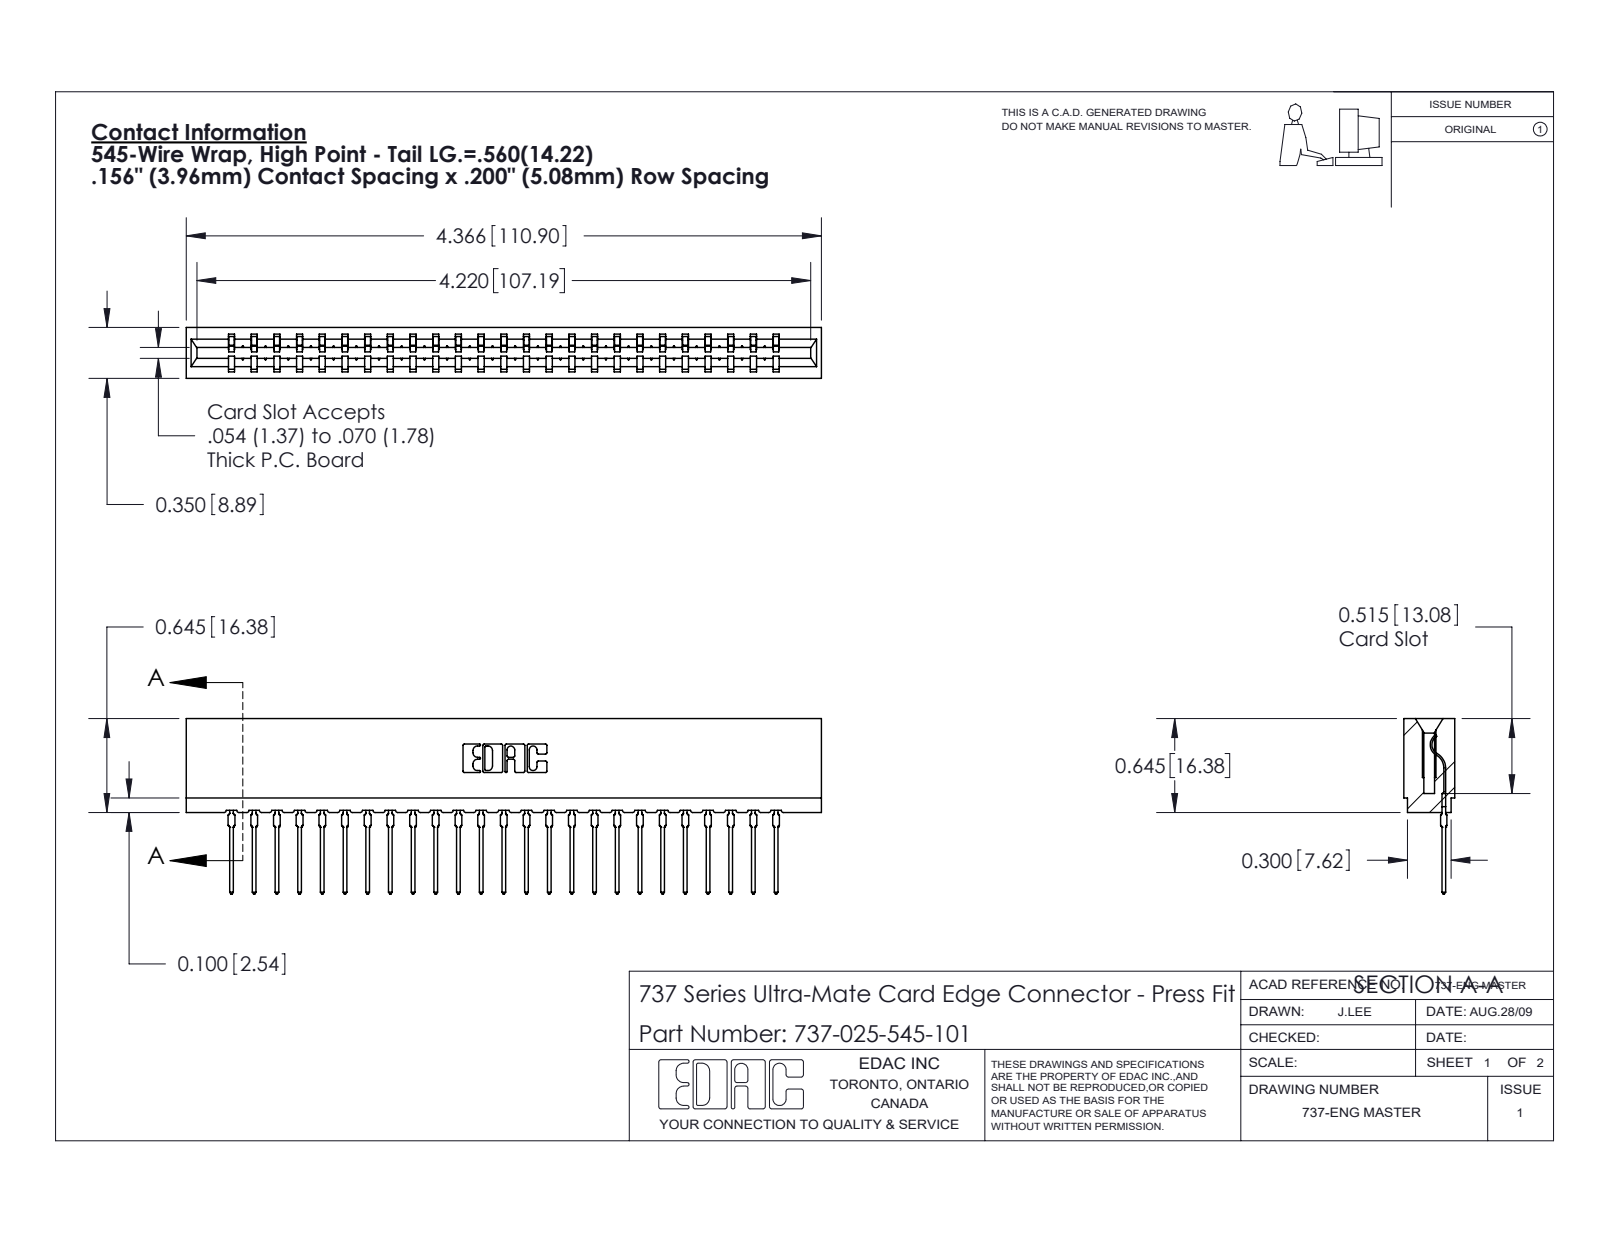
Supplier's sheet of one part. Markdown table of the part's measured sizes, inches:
| quantity | value |
| --- | --- |
| part name | 737 Part_Insulator Option - 01; 737-025-545-101; 745-292-001_545 |
| STEP written by | SolidWorks 2020 (CONFIG_CONTROL_DESIGN) |
| units | inches |
| bodies | 26 solids, 2919 faces (1754 planar, 515 cylindrical, 650 other) |
| overall size | 4.366 × 1.206 × 0.35 |
| volume | 0.666 in³ |
| surface area | 22.86 in² |
| partial cylindrical surfaces (radius × count) | 0.015 × 50, 0.021 × 50, 0.01 × 22, 0.007 × 6, 0.031 × 6, 0.005 × 4, 0.011 × 4, 0.026 × 3 |
| main face-to-face distances | 0.138, 0.212, 0.35, 0.156, 0.624, 0.074, 0.468, 0.78, 0.045, 0.305 |
